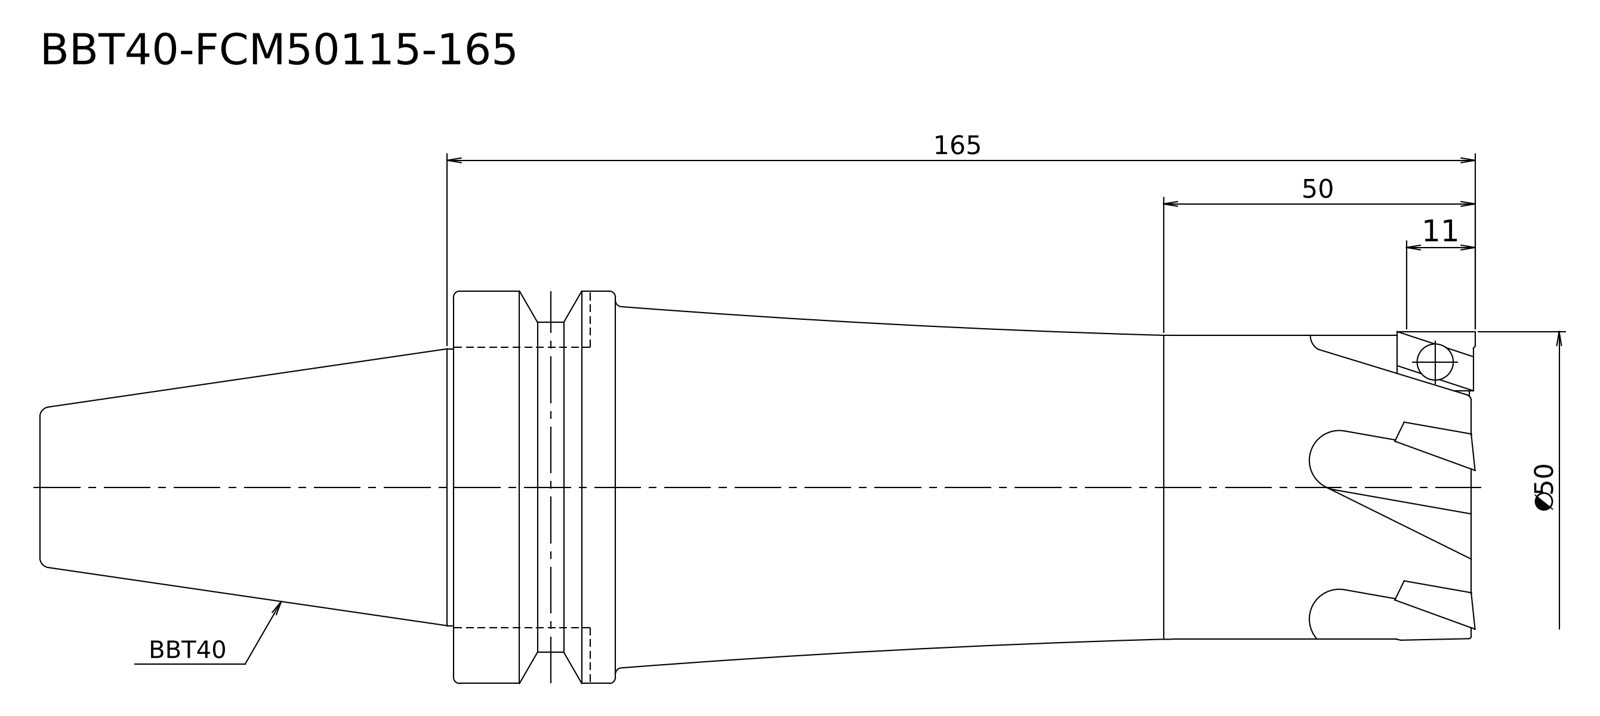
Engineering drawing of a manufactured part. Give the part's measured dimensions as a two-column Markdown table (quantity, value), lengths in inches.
| quantity | value |
| --- | --- |
| STEP written by | Kubotek KeyCreator V8.5.1 (14335) (CONFIG_CONTROL_DESIGN) |
| units | inches |
| bodies | 1 solid, 17 faces (4 planar, 6 cylindrical, 7 other) |
| overall size | 9.071 × 2.48 × 2.48 |
| volume | 26.4 in³ |
| surface area | 62.44 in² |
| round bosses / shafts (diameter × count) | 2.48 × 1, 2.087 × 1, 1.969 × 1, 1.921 × 1, 1.75 × 1 |
| main face-to-face distances | 6.457, 9.071, 2.614, 5.433, 1.024, 3.638 |
